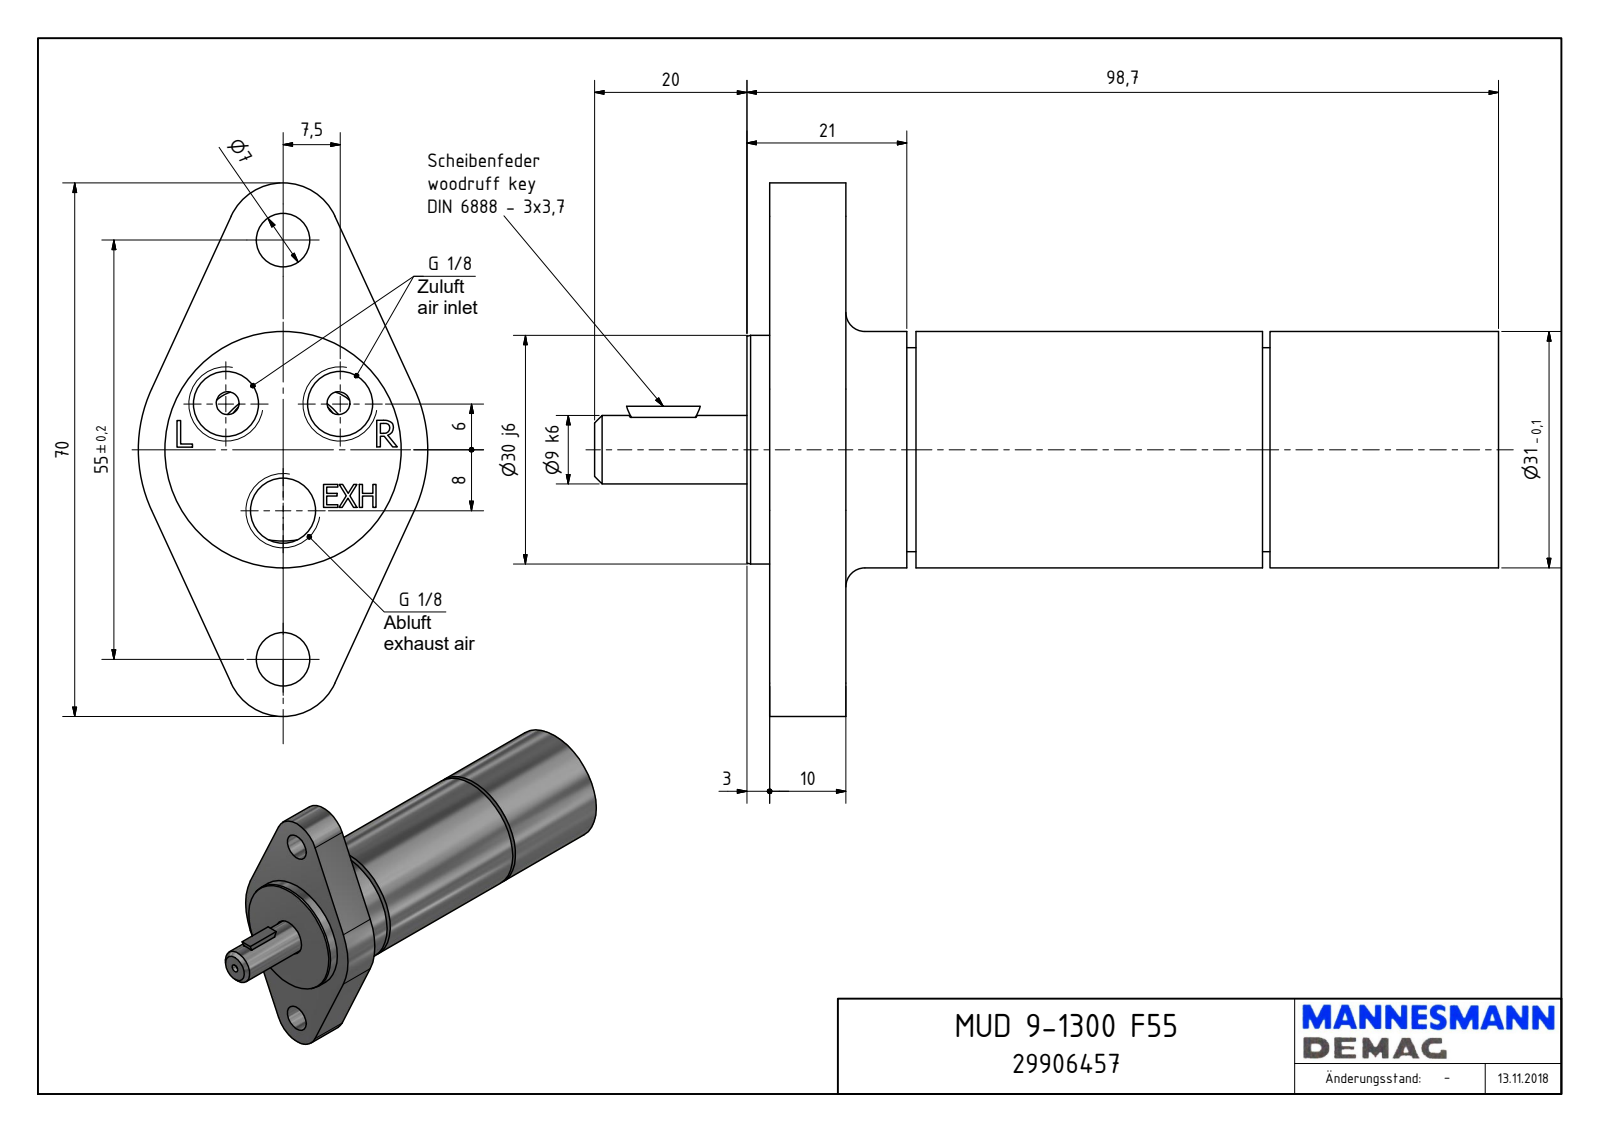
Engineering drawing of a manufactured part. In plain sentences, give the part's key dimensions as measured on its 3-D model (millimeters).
The part is named "MUD 9-1300 F55_29906457". Its 3-D file was written by "Autodesk Inventor 2018 (AUTOMOTIVE_DESIGN)". It is 1 solid with 152 faces: 94 planar, 27 cylindrical and 31 other. Overall it measures 118.7 by 70 by 38 millimeters. Its volume is 82 914 cubic millimeters and its surface area 16 831 square millimeters. Round holes: 3 of diameter 8.57, 2 of diameter 7, 1 of diameter 1, 1 of diameter 9.5, 1 of diameter 10.36, 1 of diameter 16, 1 of diameter 26.92. Round bosses or shafts: 1 of diameter 31, 1 of diameter 30, 1 of diameter 26.78, 1 of diameter 9. Partial cylindrical surfaces (rounded edges, fillets, slot ends): 2 of radius 7.5, 1 of radius 5, 1 of radius 5.25, 1 of radius 19. The main face-to-face distances are 10, 3, 13, 95.7, 98.7, 85.7, 37.98, 64.7, 9.2, 22.2. The hole center spacings are 9.6, 15.88, 22.77, 27.5, 34.33, 8, 15, 19.5.
